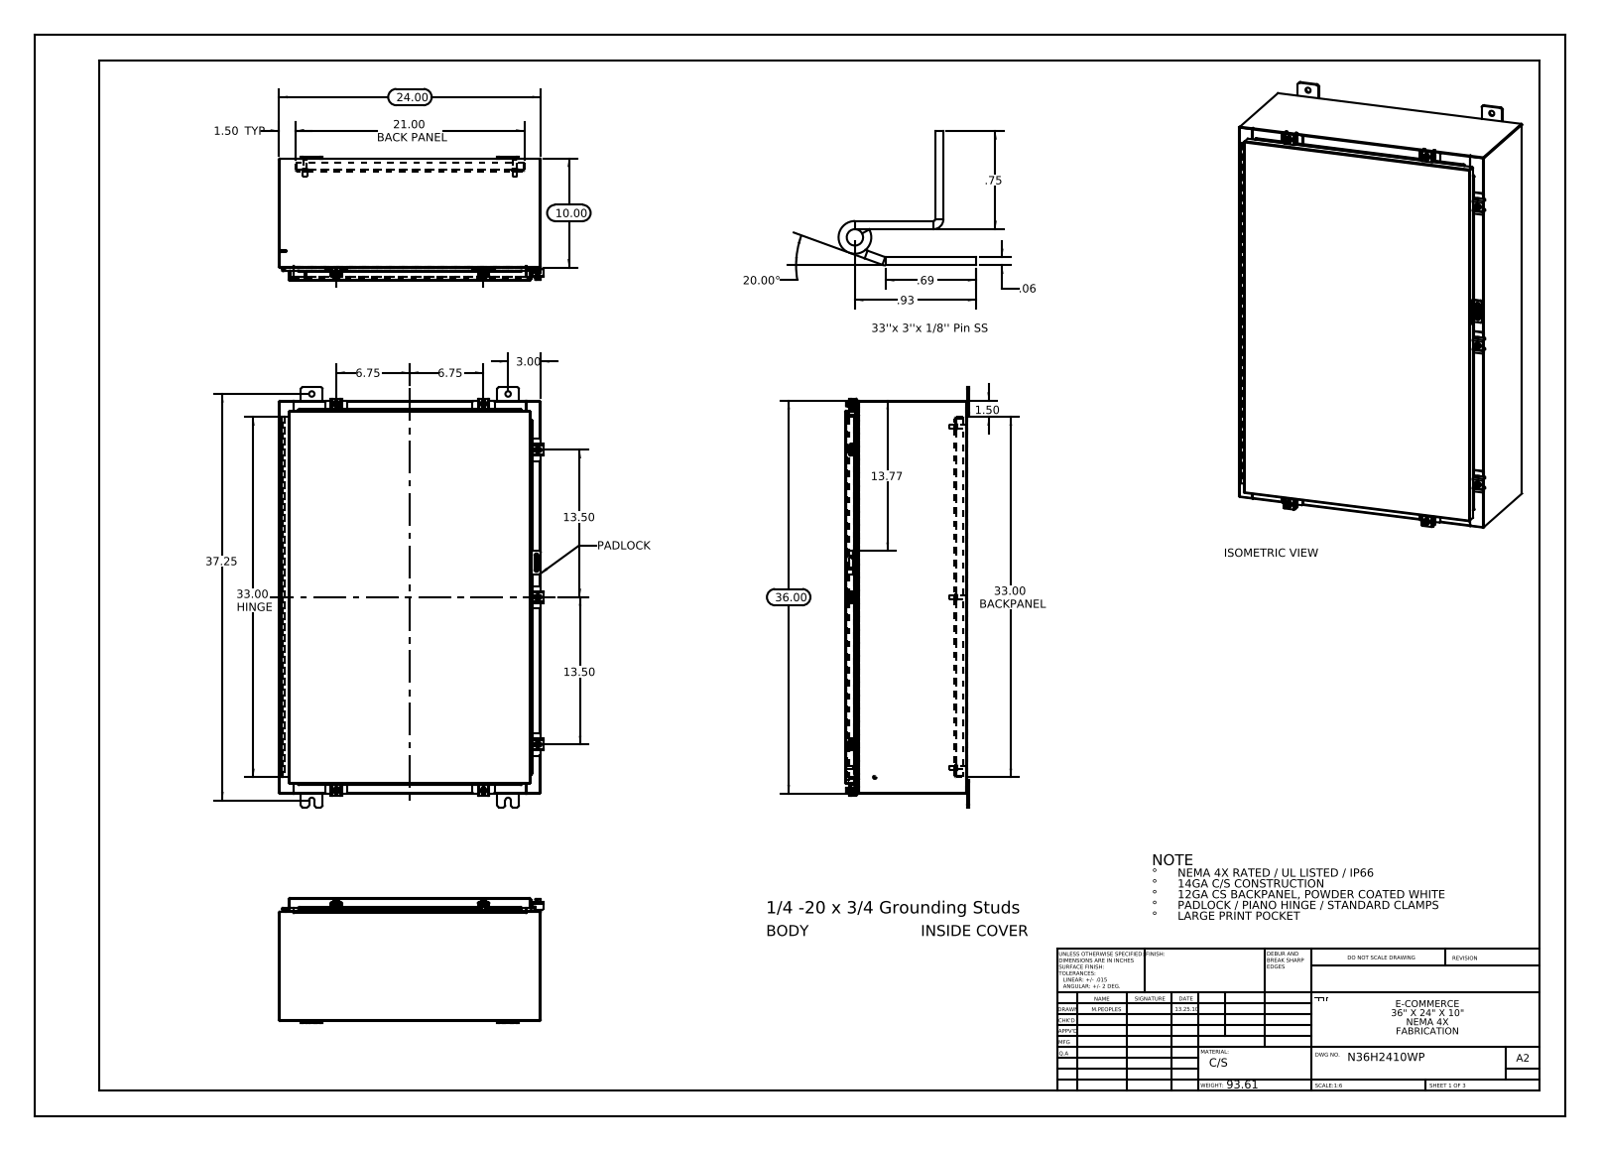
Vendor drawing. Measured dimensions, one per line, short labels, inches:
name: N36H2410SSWP Hinge Cover Side; N36H2410WP; N36H2410SSWP Top; N36H2410SSWP Hinge Enclosure Side2 (+8 more)
written by: SolidWorks 2013 (CONFIG_CONTROL_DESIGN)
unit: in
bodies: 56 solids, 2210 faces (1144 planar, 930 cylindrical, 136 other)
size: 38.5 × 24.211 × 11.389
volume: 328.5 in³; area: 8 227 in²
holes: 10× ⌀0.5, 7× ⌀0.213, 7× ⌀0.26, 2× ⌀0.125
bosses: 8× ⌀0.25, 7× ⌀0.5, 7× ⌀0.399, 6× ⌀0.625, 6× ⌀0.375, 6× ⌀0.33, 2× ⌀0.315, 2× ⌀0.236
rounds: 34× R0.06, 27× R0.013, 24× R0.19, 21× R0.088, 14× R0.12, 14× R0.141, 11× R0.05, 10× R0.08
face distances: 0.075, 11.126, 11.051, 11.201, 0.104, 23.925, 1, 1.075, 10.051, 10.126
hole spacings: 13.5, 15.625, 17.957, 24.793, 33.474, 37.154, 19.25, 1.858
